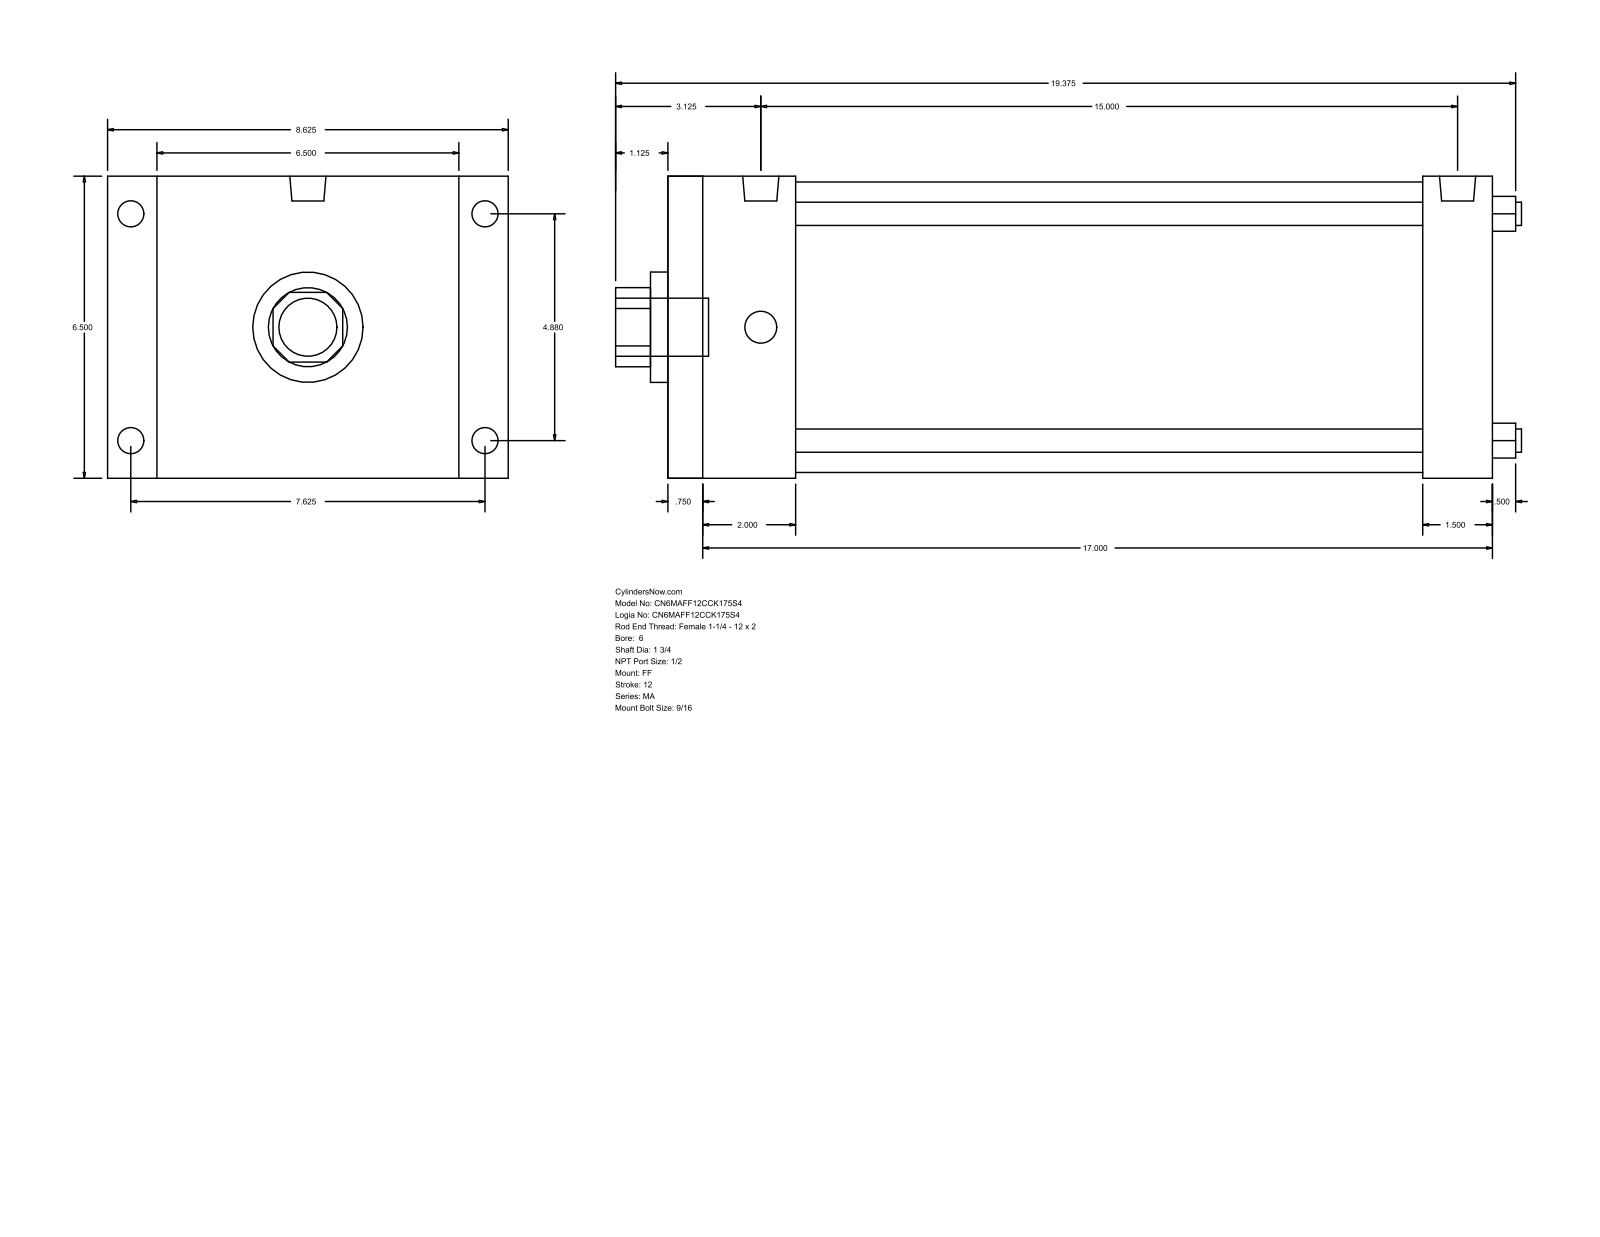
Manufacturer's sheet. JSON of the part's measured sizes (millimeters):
{"part_name": "MA_FF__0600_1.75", "step_written_by": "GSSL Pune (CONFIG_CONTROL_DESIGN)", "units": "millimeters", "bodies": {"solids": 0, "faces": 92, "planar": 64, "cylindrical": 28, "other": 0}, "overall_size": [495.3, 219.07, 165.1], "round_holes": [[12.7, 4], [44.45, 1], [60.33, 1], [158.75, 1]], "round_bosses_or_shafts": [[17.46, 4], [14.29, 4], [19.77, 2], [31.75, 1]], "partial_cylinders_radius": [[21.63, 1]], "face_to_face_distances": [165.1, 450.86, 19.05, 431.81, 50.8, 393.7, 69.85, 381.01, 412.75, 342.9], "hole_center_spacings": [87.65, 123.96, 175.31]}
